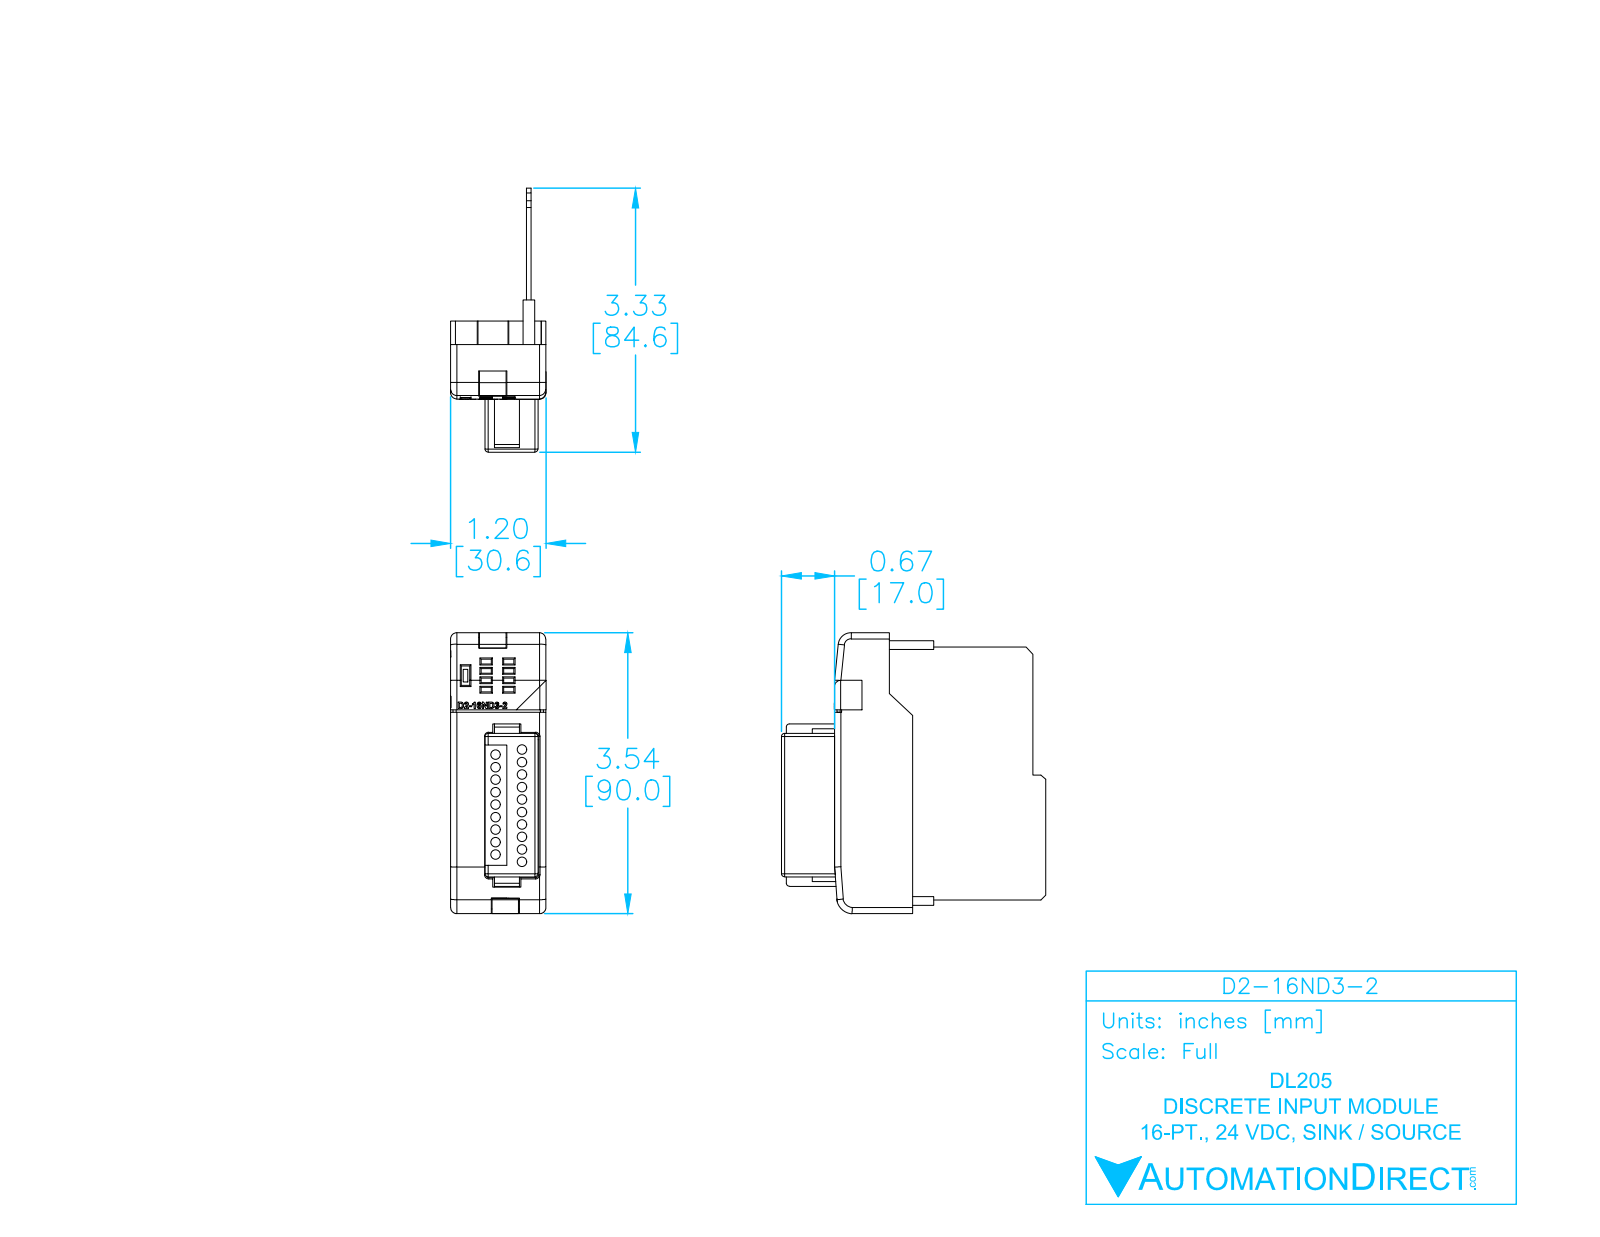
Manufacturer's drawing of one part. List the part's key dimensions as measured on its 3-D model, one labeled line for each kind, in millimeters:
Part name (STEP PRODUCT): D2-16ND3-2_ModuleCase Light_NEW
STEP written by: SolidWorks 2009 (AUTOMOTIVE_DESIGN)
Units: millimetres
Bodies: 2 solids, 655 faces (412 planar, 158 cylindrical, 85 other)
Overall size (bounding box): 90 × 84.6 × 30.55
Volume: 30 557 mm³ · Surface area: 32 610 mm²
Round holes (diameter × count): ⌀3 ×19
Partial cylindrical surfaces — rounded edges, fillets, slot ends (radius × count): R0.35 ×28, R1 ×18, R0.5 ×12, R2 ×11, R0.25 ×6, R2.62 ×1, R3.79 ×1, R4.12 ×1
Main face-to-face distances: 1.5, 4.72, 3.22, 6.22, 0.5, 1, 24.28, 29, 18, 11
Hole centre spacings: 4, 8, 12, 16, 8.61, 8.77, 20, 10.16
